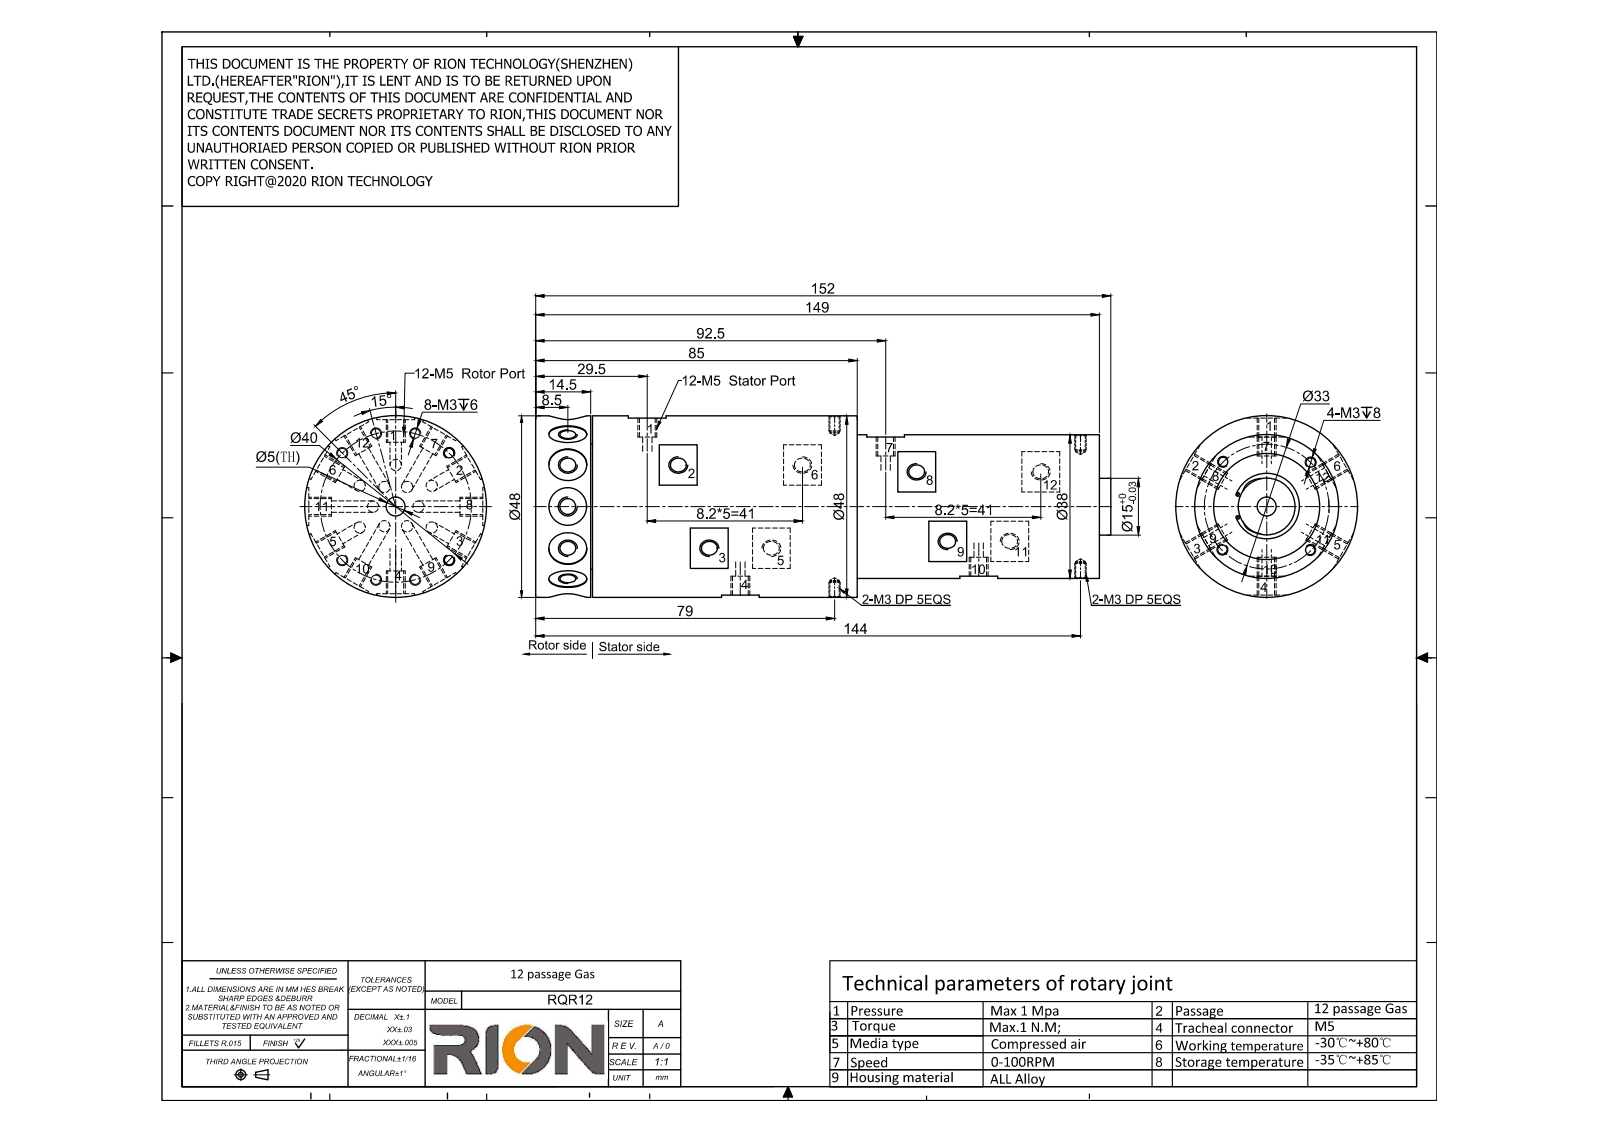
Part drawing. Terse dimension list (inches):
name: RQR12
written by: SolidWorks 2014 (CONFIG_CONTROL_DESIGN)
unit: in
bodies: 1 solid, 345 faces (87 planar, 174 cylindrical, 84 other)
size: 5.984 × 1.89 × 1.89
volume: 13.31 in³; area: 51.68 in²
holes: 20× ⌀0.098, 18× ⌀0.165, 16× ⌀0.118, 6× ⌀0.394, 1× ⌀0.197, 1× ⌀1.102
bosses: 1× ⌀1.89, 1× ⌀1.496, 1× ⌀1.299, 1× ⌀0.591
face distances: 0.02, 0.571, 0.591, 3.346, 2.776, 2.756, 5.866, 5.295, 5.276, 2.52
hole spacings: 0.787, 1.021, 1.521, 0.969, 2.48, 0.137, 0.386, 0.395
